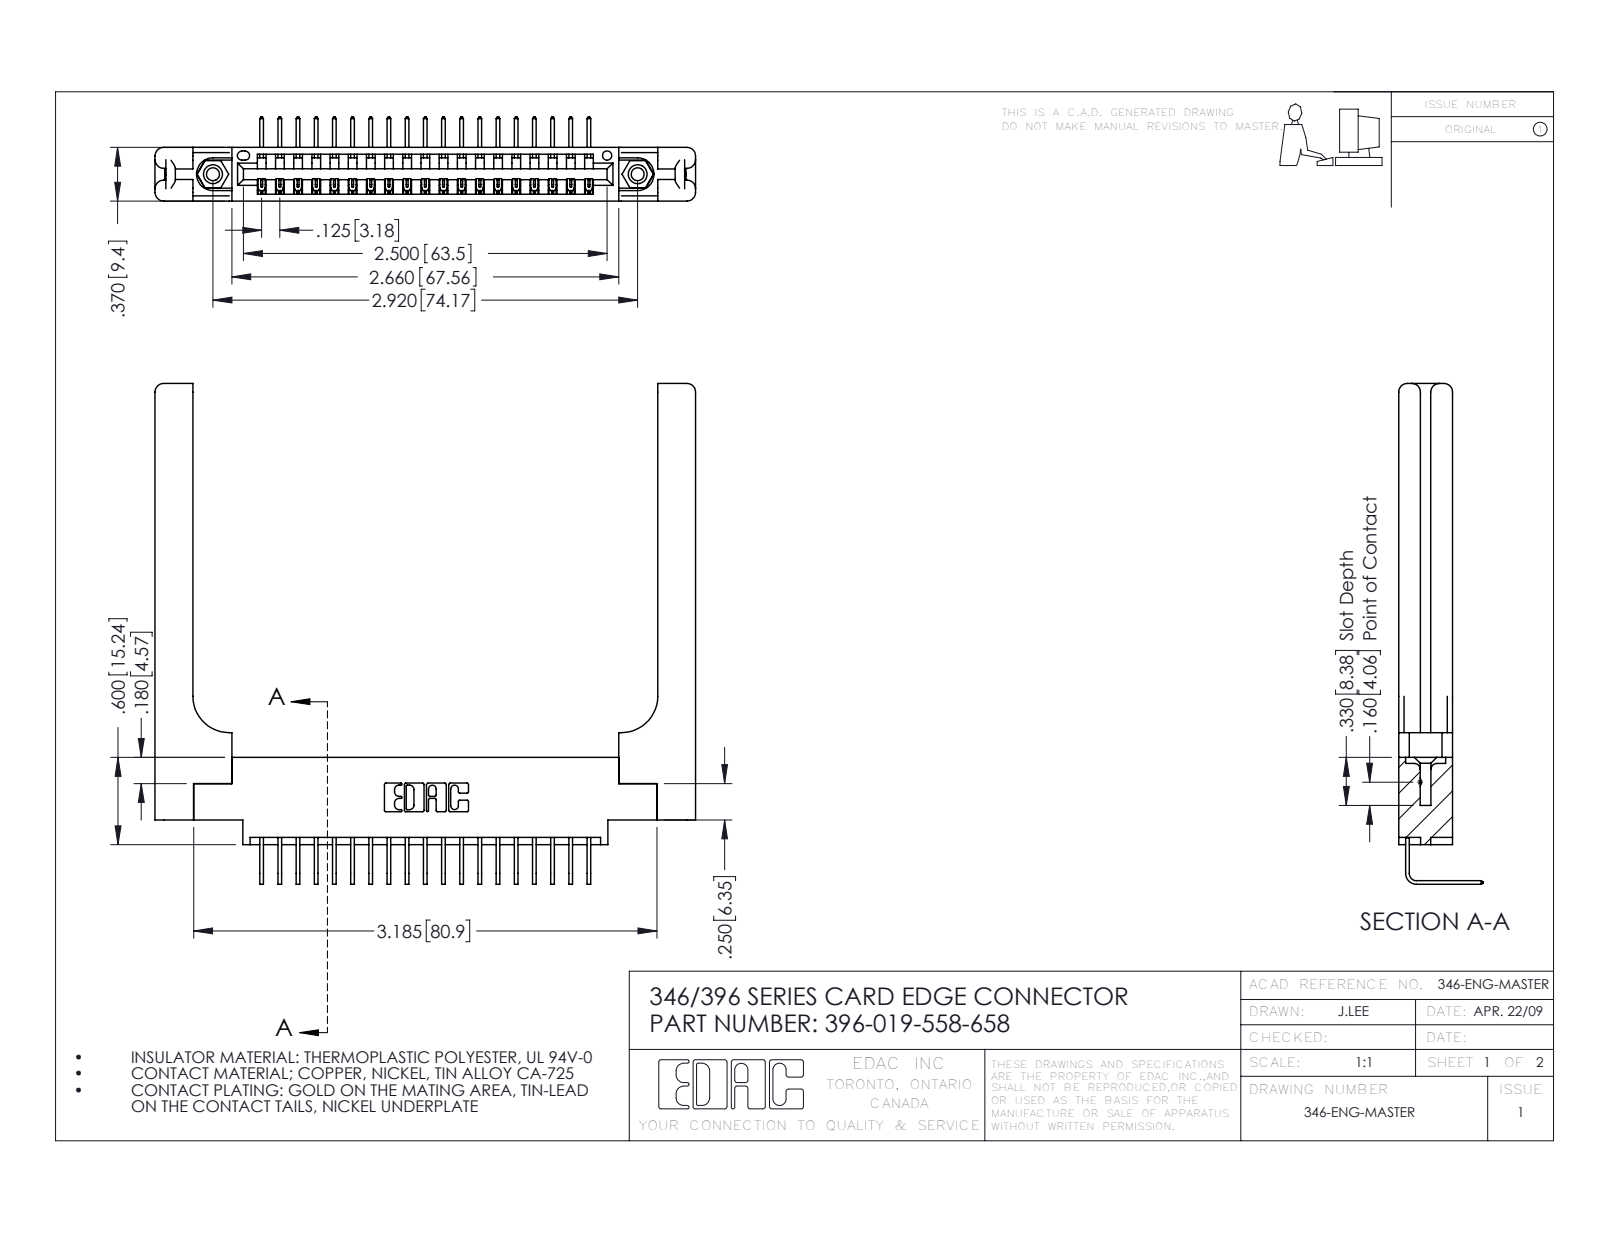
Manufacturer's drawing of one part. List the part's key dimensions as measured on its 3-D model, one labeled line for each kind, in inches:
Part name (STEP PRODUCT): 346-220-058_345-220-058; 396-019-558-658; 345-292-001_558 Tail - 2; 346 Part_0.170 Offset - 0.156 Dia-TH (+1 more)
STEP written by: SolidWorks 2016 (CONFIG_CONTROL_DESIGN)
Units: inches
Bodies: 24 solids, 1522 faces (1026 planar, 436 cylindrical, 60 other)
Overall size (bounding box): 3.716 × 3.443 × 0.58
Volume: 0.995 in³ · Surface area: 25.48 in²
Round holes (diameter × count): ⌀0.089 ×2, ⌀0.125 ×2, ⌀0.156 ×2, ⌀0.064 ×1
Round bosses / shafts (diameter × count): ⌀0.155 ×2
Partial cylindrical surfaces — rounded edges, fillets, slot ends (radius × count): R0.006 ×38, R0.01 ×22, R0.06 ×16, R0.007 ×6, R0.031 ×6, R0.026 ×3, R0.03 ×2, R0.031 ×2
Main face-to-face distances: 0.37, 0.072, 0.15, 0.322, 0.148, 0.048, 0.25, 0.025, 0.298, 0.102
Hole centre spacings: 0.246, 2.713, 2.92
